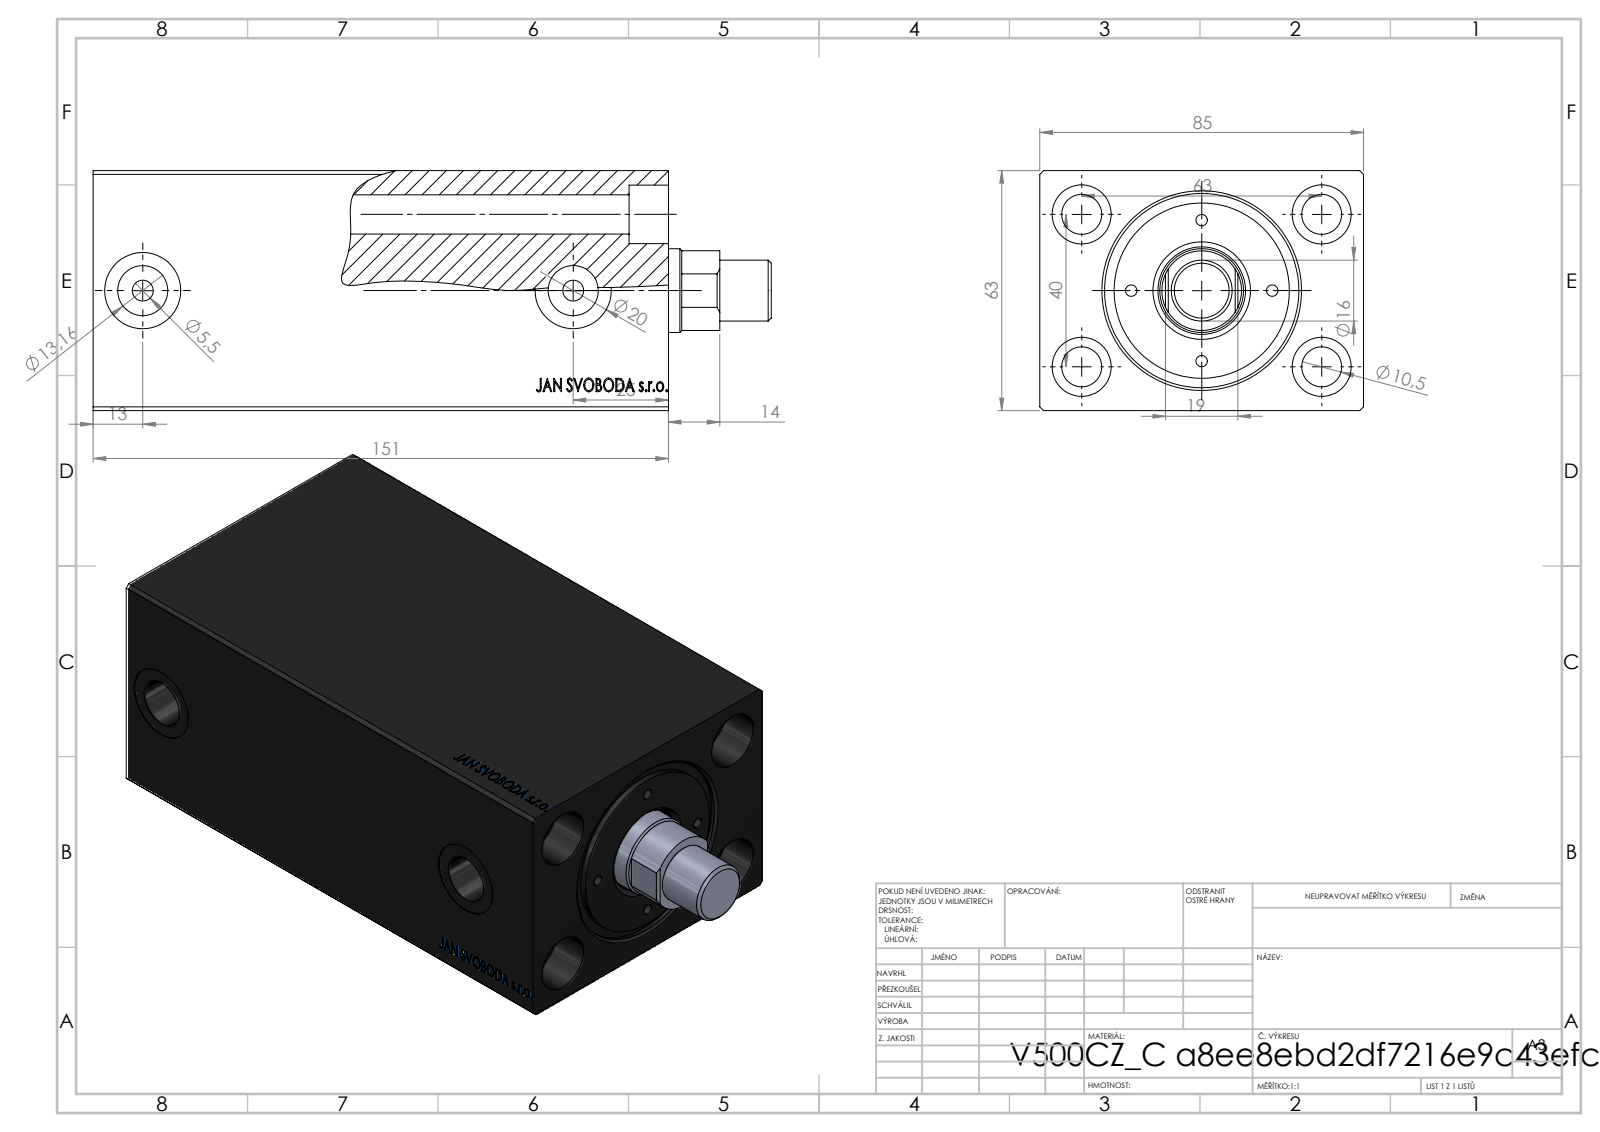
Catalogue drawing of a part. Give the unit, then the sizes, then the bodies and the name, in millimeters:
Units: millimetres
Overall size (bounding box): 178 × 85 × 63
Round holes (diameter × count): ⌀3 ×4, ⌀10.5 ×4, ⌀15.5 ×4, ⌀5.5 ×2, ⌀13.16 ×2, ⌀20 ×2, ⌀16 ×1, ⌀22 ×1, ⌀23 ×1, ⌀36 ×1, ⌀40 ×1, ⌀51 ×1
Round bosses / shafts (diameter × count): ⌀46 ×1, ⌀14 ×1
Partial cylindrical surfaces — rounded edges, fillets, slot ends (radius × count): R10.46 ×1
Main face-to-face distances: 63, 85, 151, 115, 36, 11.8, 103.2, 139.2, 10, 1.8
Hole centre spacings: 18.5, 23.85, 26.16, 31.54, 37.31, 49.74, 53.85, 37
Volume: 680 535 mm³ · Surface area: 113 487 mm²
Bodies: 4 solids, 884 faces (413 planar, 71 cylindrical, 400 other)
Part name (STEP PRODUCT): V500CZ_MALE_METRIC; V500CZ_VCP_C; V500CZ_VC_vysunovaci_C; V500CZ_C
STEP written by: SolidWorks 2019 (CONFIG_CONTROL_DESIGN)
